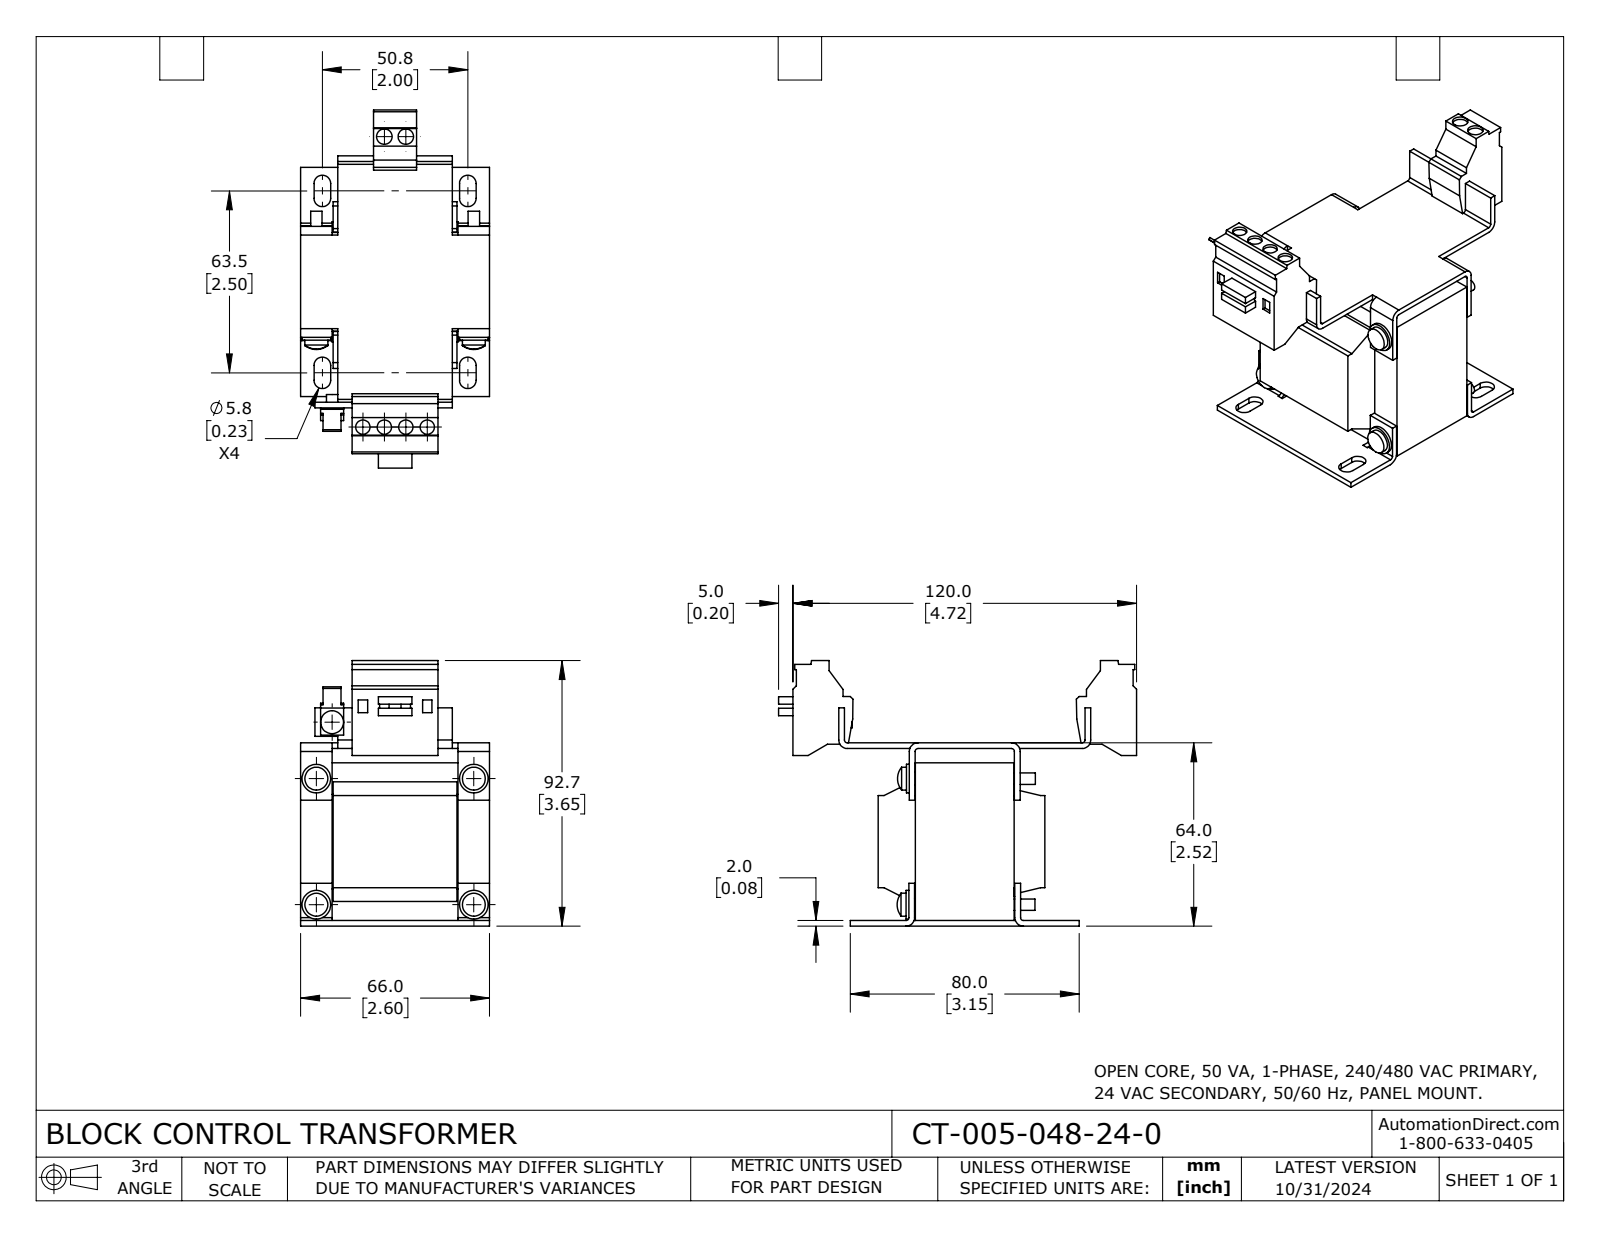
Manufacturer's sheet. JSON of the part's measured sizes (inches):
{"part_name": "CT-005-048-24-0", "step_written_by": "SolidWorks 2023 (CONFIG_CONTROL_DESIGN)", "units": "inches", "bodies": {"solids": 1, "faces": 325, "planar": 229, "cylindrical": 92, "other": 4}, "overall_size": [4.921, 3.65, 2.598], "volume_in3": 12.63, "surface_area_in2": 85.75, "round_holes": [[0.197, 4], [0.213, 2]], "round_bosses_or_shafts": [[0.315, 5], [0.157, 5], [0.394, 4], [0.177, 4]], "partial_cylinders_radius": [[0.114, 8], [0.039, 6], [0.118, 6]], "face_to_face_distances": [0.079, 2.441, 2.165, 0.433, 2.52, 0.448, 2.15, 2.362, 0.276, 1.732], "hole_center_spacings": [0.295, 4.003, 0.591, 3.992, 4.035, 0.886]}
